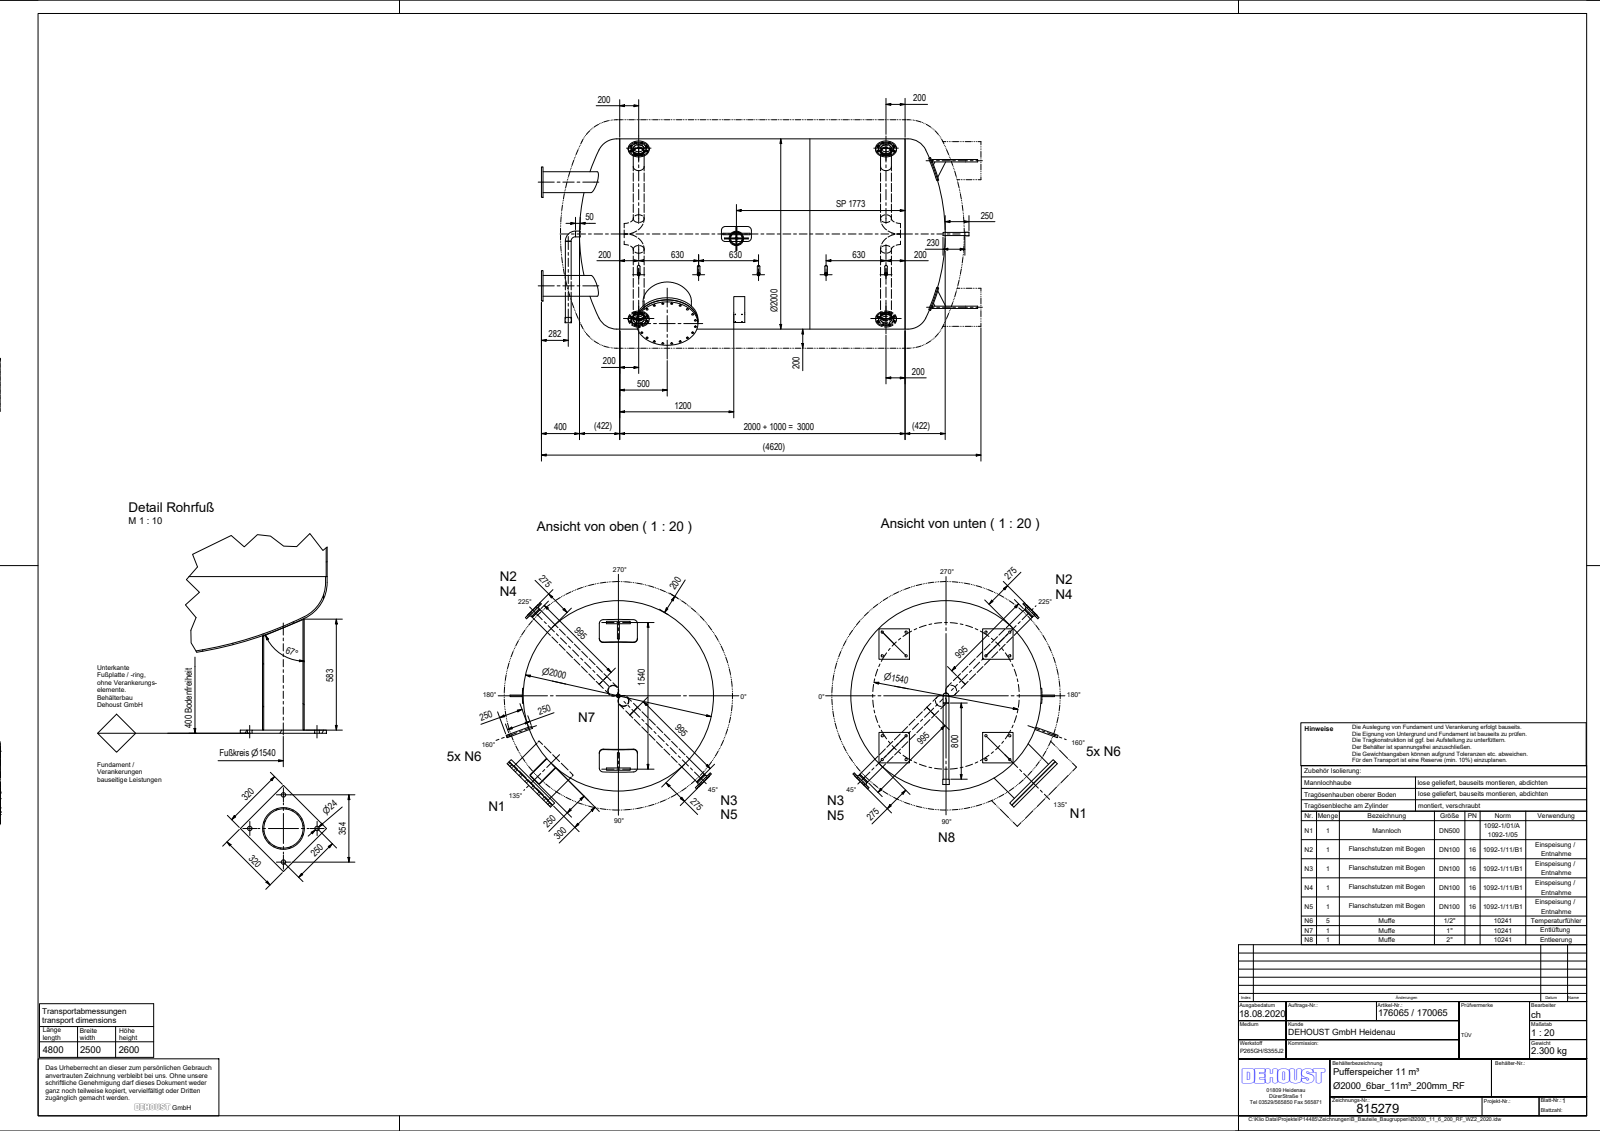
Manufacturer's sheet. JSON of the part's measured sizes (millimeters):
{"part_name": "Ø2000_11_6_200_RF_WZ2_2020; Klöpper_Gew_Ø2000_7 ,8; Zyl_Ø2000_5x3000_2020; TÖB_Puffer_Ø2000_7,8_200 (+8 more)", "step_written_by": "Autodesk Inventor 2019 (AUTOMOTIVE_DESIGN)", "units": "millimeters", "bodies": {"solids": 52, "faces": 404, "planar": 170, "cylindrical": 208, "other": 26}, "overall_size": [4585.48, 2179.13, 2169.2], "volume_mm3": 272200000, "surface_area_mm2": 66700000, "round_holes": [[18, 32], [22, 32], [24, 16], [18.63, 5], [21.7, 5], [26.9, 5], [5.8, 4], [106.3, 4], [107.1, 4], [114.3, 4], [206.5, 4], [52.3, 2]], "round_bosses_or_shafts": [[26.9, 5], [26.4, 5], [220, 4], [219.1, 4], [158, 4], [114.3, 4], [645, 2], [2000, 1]], "partial_cylinders_radius": [[42, 12], [10, 4], [5, 2], [6, 2], [36, 1], [72, 1], [125, 1], [1009, 1]], "face_to_face_distances": [400, 16, 28, 25, 557.5, 957.5, 582.5, 982.5, 1540, 2072.45], "hole_center_spacings": [90, 300, 2600, 93.86, 185.41, 352.67, 592.61, 127.28]}
